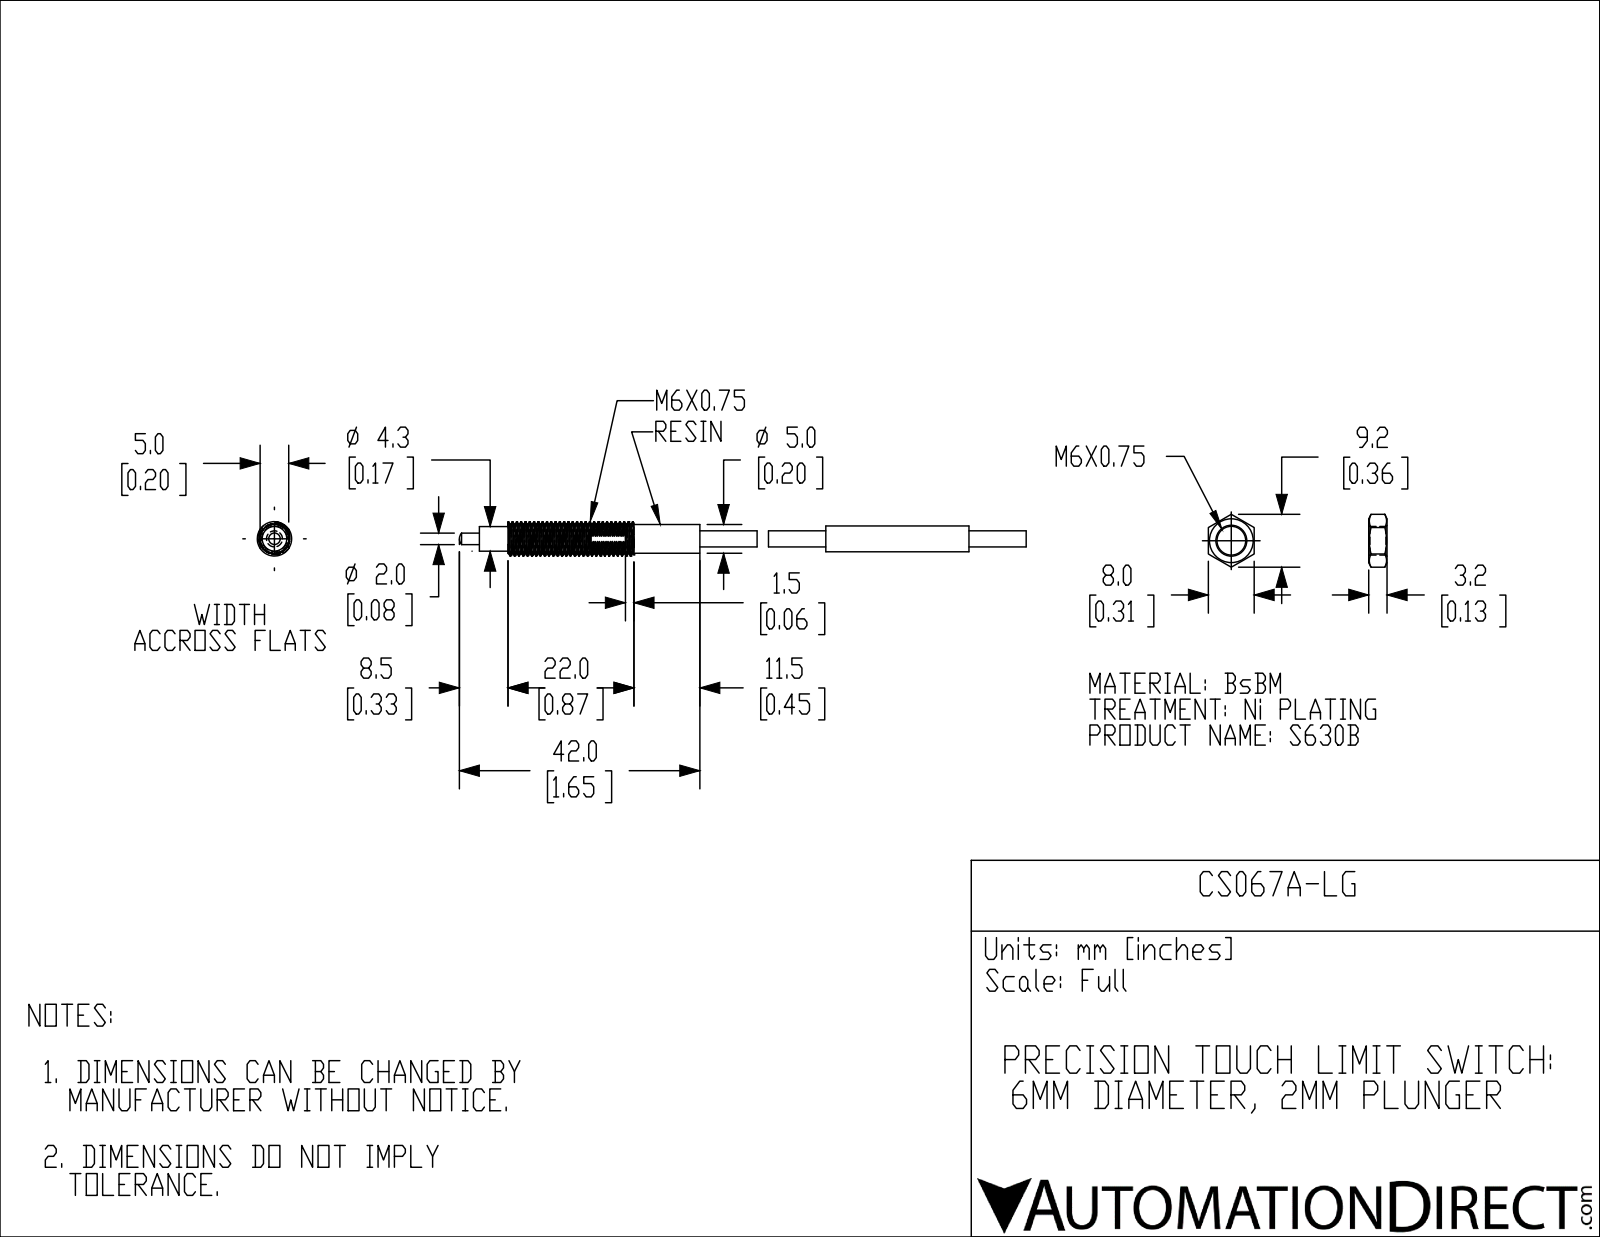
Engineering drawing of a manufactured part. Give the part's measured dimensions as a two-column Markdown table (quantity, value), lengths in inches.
| quantity | value |
| --- | --- |
| part name | CS067A-LG |
| STEP written by | SolidWorks 2018 (AUTOMOTIVE_DESIGN) |
| units | inches |
| bodies | 2 solids, 91 faces (15 planar, 25 cylindrical, 51 other) |
| overall size | 3.898 × 0.236 × 0.236 |
| volume | 0.086 in³ |
| surface area | 2.462 in² |
| round bosses / shafts (diameter × count) | 0.236 × 1, 0.197 × 1, 0.177 × 1, 0.169 × 1, 0.11 × 1, 0.079 × 1 |
| main face-to-face distances | 0.197, 0.394, 1.85, 0.866, 1.319, 1.378, 0.472, 1.516, 0.984, 2.382 |
